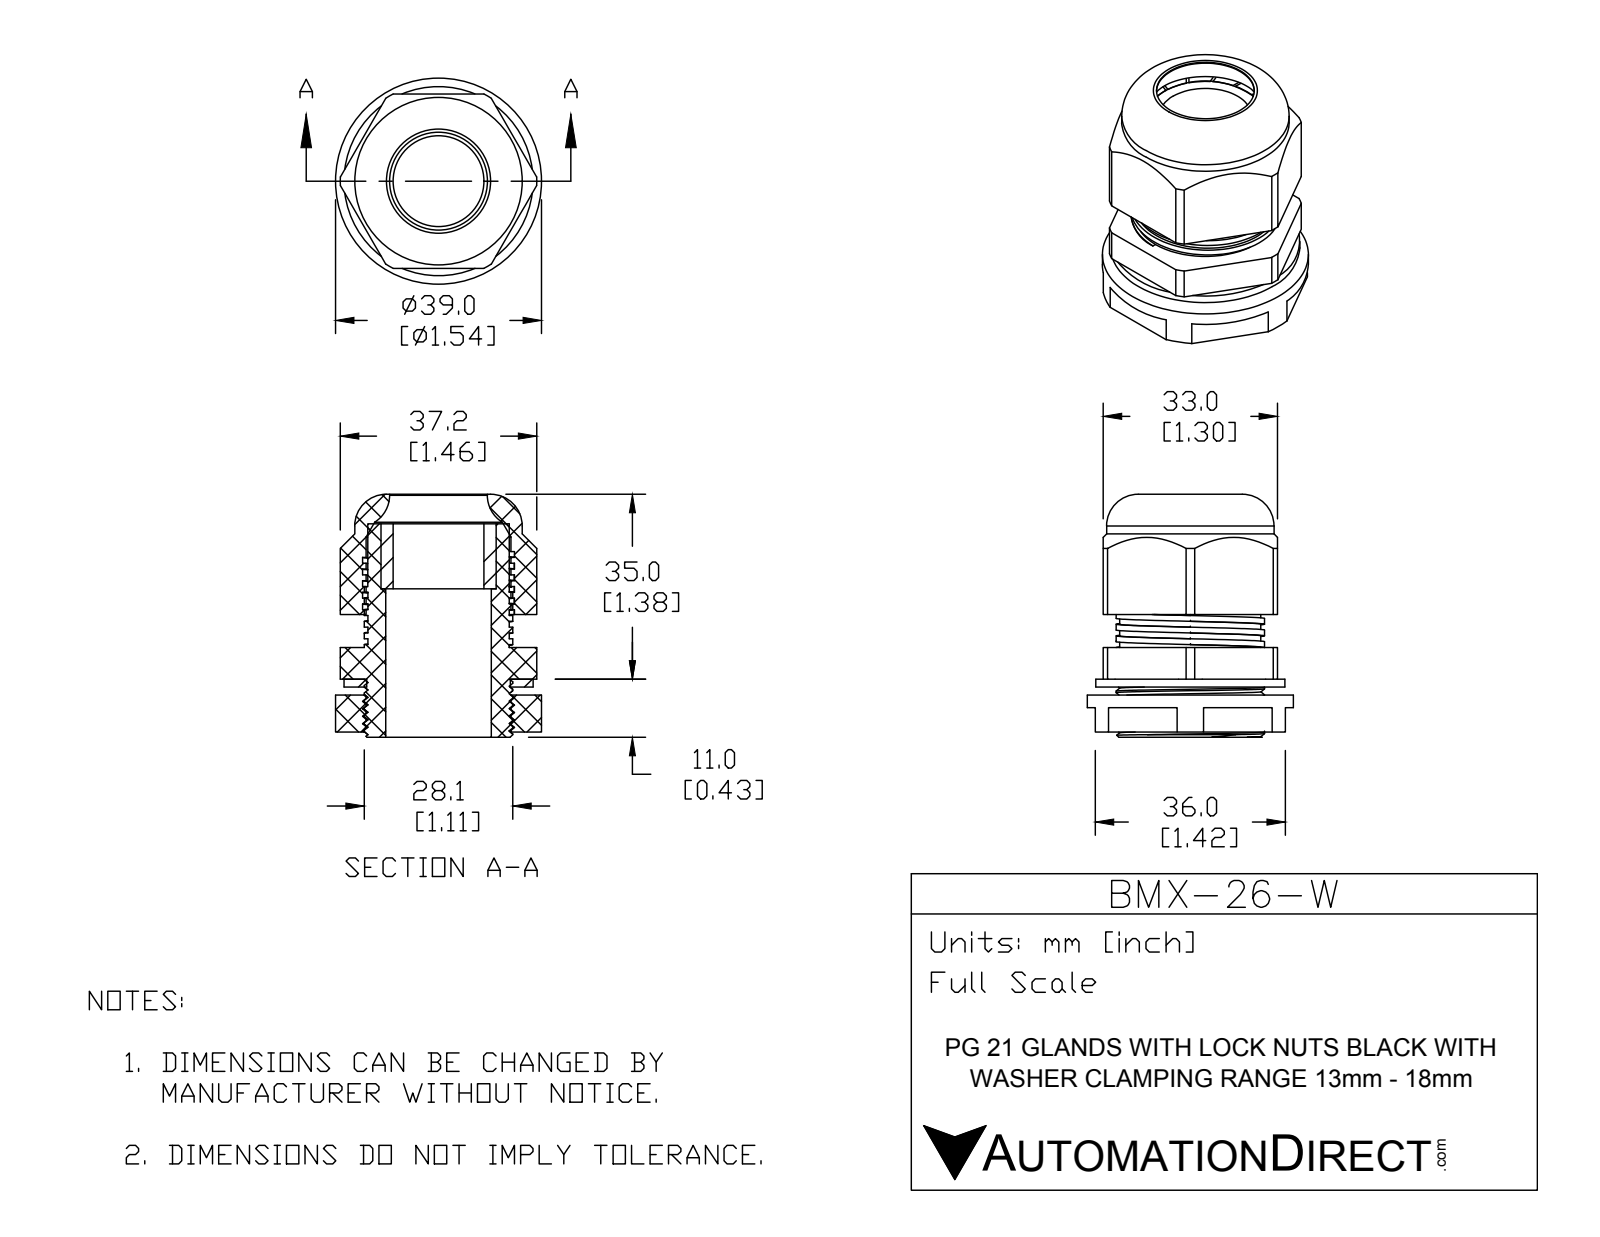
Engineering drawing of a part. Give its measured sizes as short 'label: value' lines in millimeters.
name: BMX-26-W
written by: SolidWorks 2015 (CONFIG_CONTROL_DESIGN)
unit: mm
bodies: 5 solids, 208 faces (101 planar, 85 cylindrical, 22 other)
size: 46 × 39 × 39
volume: 25 409 mm³; area: 20 529 mm²
holes: 1× ⌀17.2, 1× ⌀18.5, 1× ⌀20, 1× ⌀21.8, 1× ⌀27.2, 1× ⌀27.43
bosses: 1× ⌀39, 1× ⌀35.8, 1× ⌀31.7, 1× ⌀28.1, 1× ⌀26.8
rounds: 1× R18.6
face distances: 1.5, 33, 9.5, 8.5, 2.5, 7, 8, 1, 34.5, 15.5
